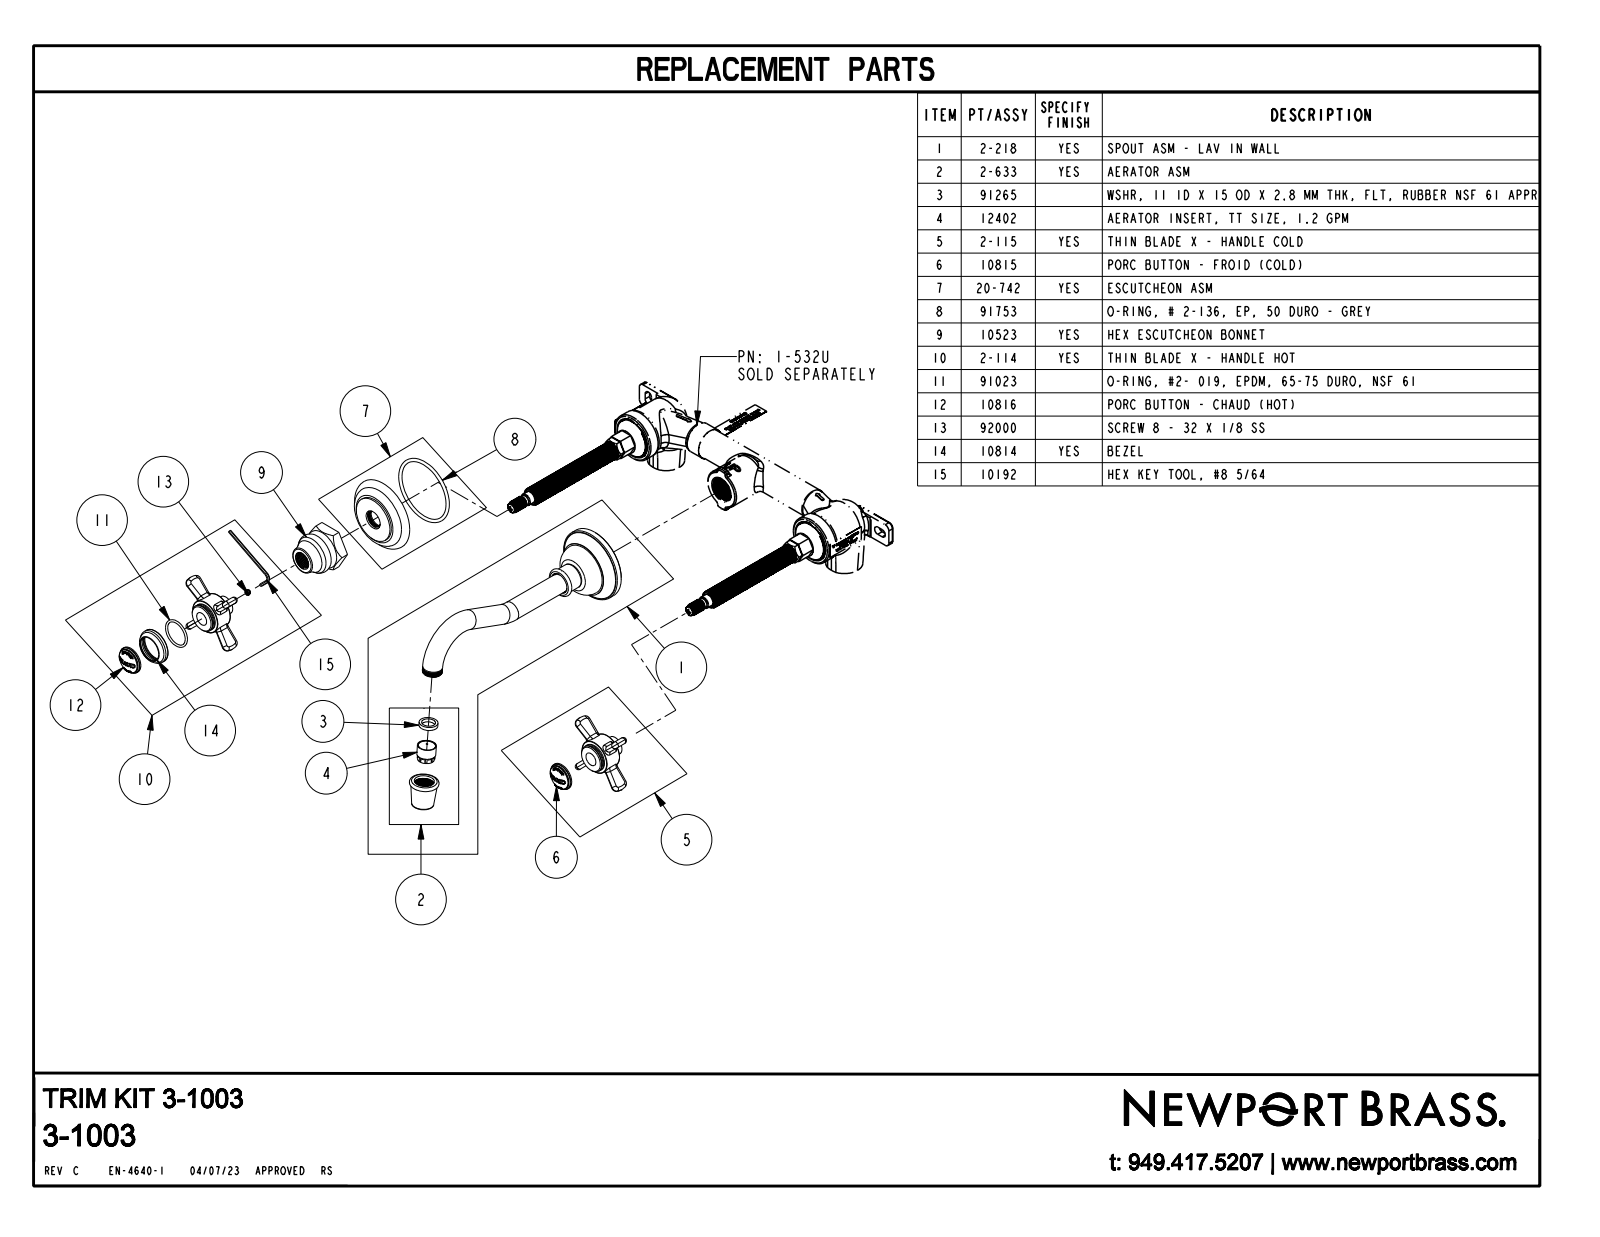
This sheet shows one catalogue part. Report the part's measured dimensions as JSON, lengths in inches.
{"part_name": "3-1003_SW0002", "step_written_by": "CREO PARAMETRIC BY PTC INC, 2018400 (AUTOMOTIVE_DESIGN)", "units": "inches", "bodies": {"solids": 5, "faces": 1097, "planar": 453, "cylindrical": 334, "other": 310}, "overall_size": [10.236, 7.645, 2.445], "volume_in3": 12.03, "surface_area_in2": 82.54, "round_holes": [[0.815, 2], [1.9, 2]], "round_bosses_or_shafts": [[1.482, 2], [1.115, 2], [1.1, 2], [0.89, 2], [0.875, 2], [0.805, 2], [0.8, 2], [0.625, 2]], "partial_cylinders_radius": [[0.1, 29], [0.011, 28], [0.025, 17], [0.006, 14], [0.005, 10], [0.015, 10], [0.006, 8], [0.014, 8]], "face_to_face_distances": [0.22, 0.2, 5.568, 2.057, 1.837, 1.313, 6.82, 5.368, 5.768, 0.375], "hole_center_spacings": [7.876]}
